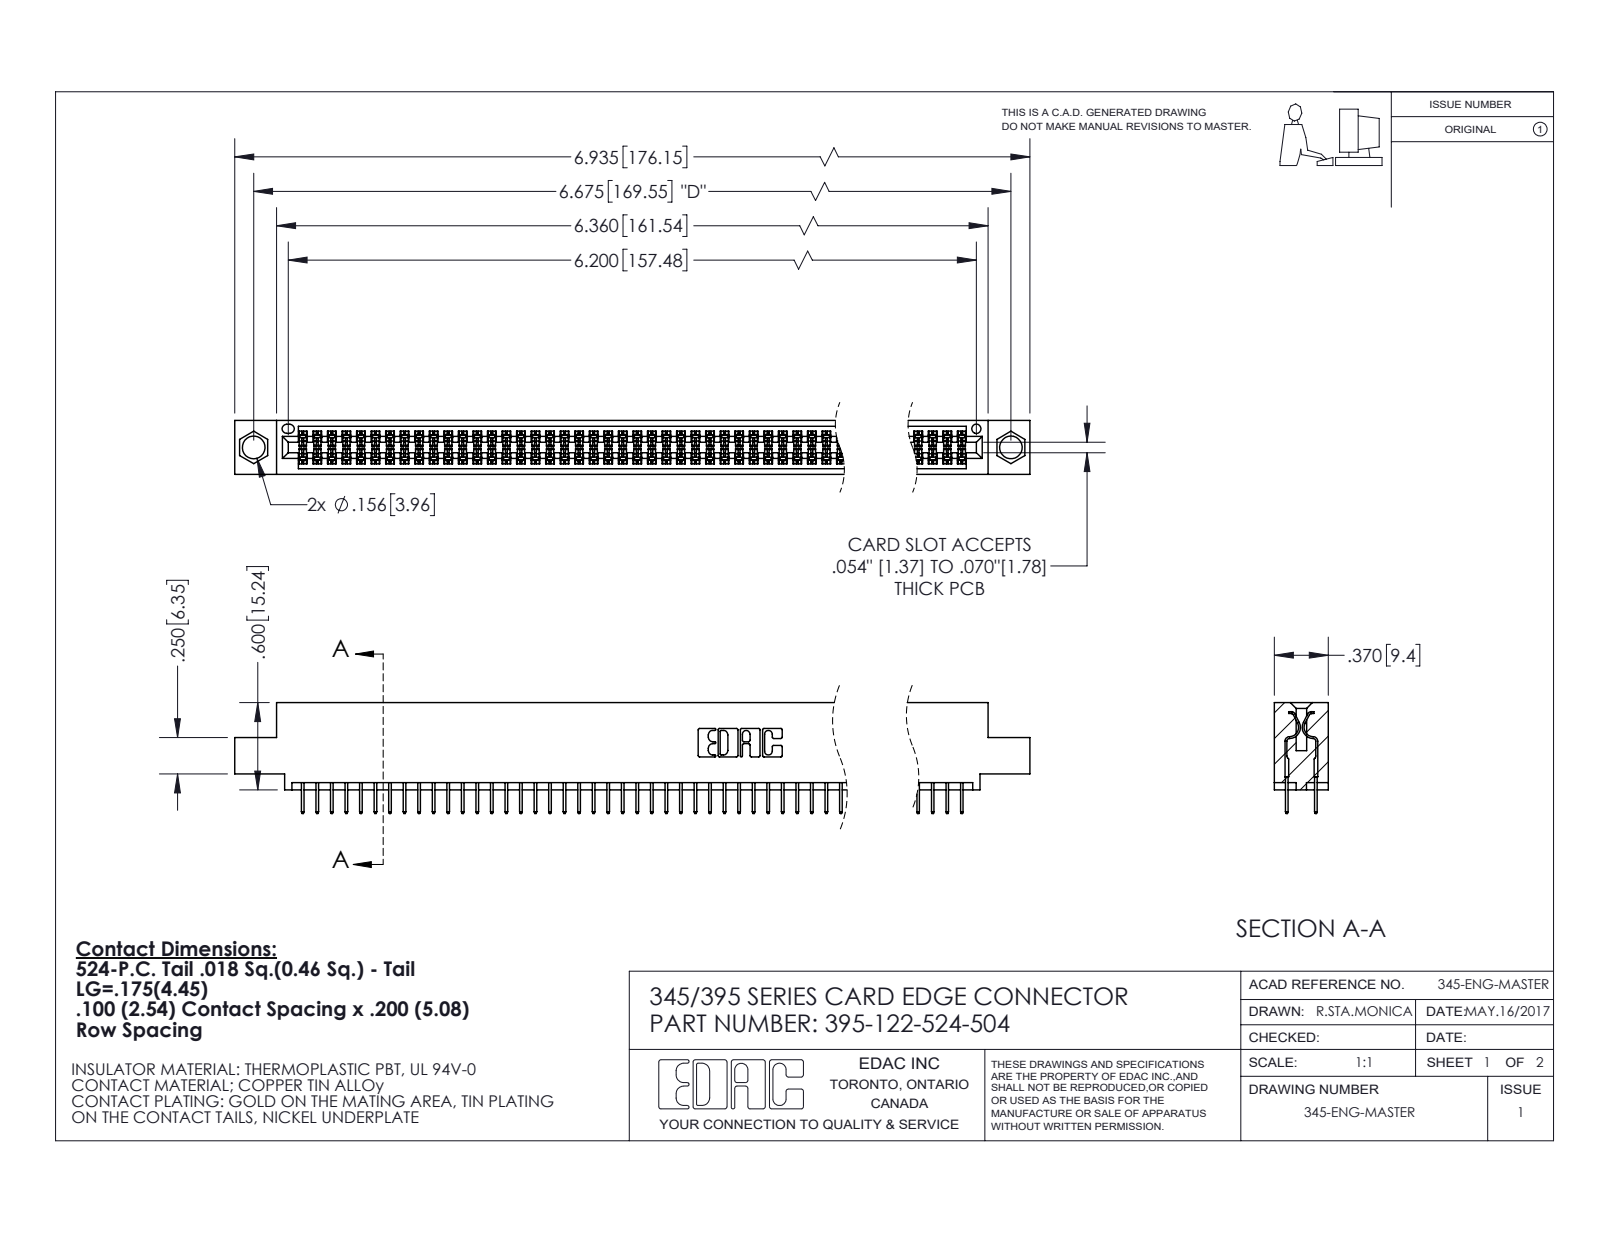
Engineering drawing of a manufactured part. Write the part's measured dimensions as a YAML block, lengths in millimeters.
part_name: "345-292-001_345-293-124; 395-122-524-504; 345 Part_0.110 Offset - 0.156 Dia-TI"
step_written_by: "SolidWorks 2020 (CONFIG_CONTROL_DESIGN)"
units: millimeters
bodies: {solids: 123, faces: 6732, planar: 4856, cylindrical: 1876, other: 0}
overall_size: [176.1, 19.4, 9.4]
volume: 16930
surface_area: 24840
round_holes:
  - {diameter: 4, count: 2}
  - {diameter: 1.6, count: 1}
partial_cylinders:
  - {radius: 0.2, count: 244}
  - {radius: 0.3, count: 22}
  - {radius: 0.2, count: 6}
  - {radius: 0.8, count: 6}
  - {radius: 0.7, count: 3}
  - {radius: 0.4, count: 2}
  - {radius: 0.5, count: 2}
  - {radius: 0.6, count: 2}
face_to_face_distances: [1.8, 7.6, 5.1, 9.4, 2.5, 6.9, 0.6, 5.7, 1.8, 4.4]
hole_center_spacings: [6.9, 163.6, 169.5]
